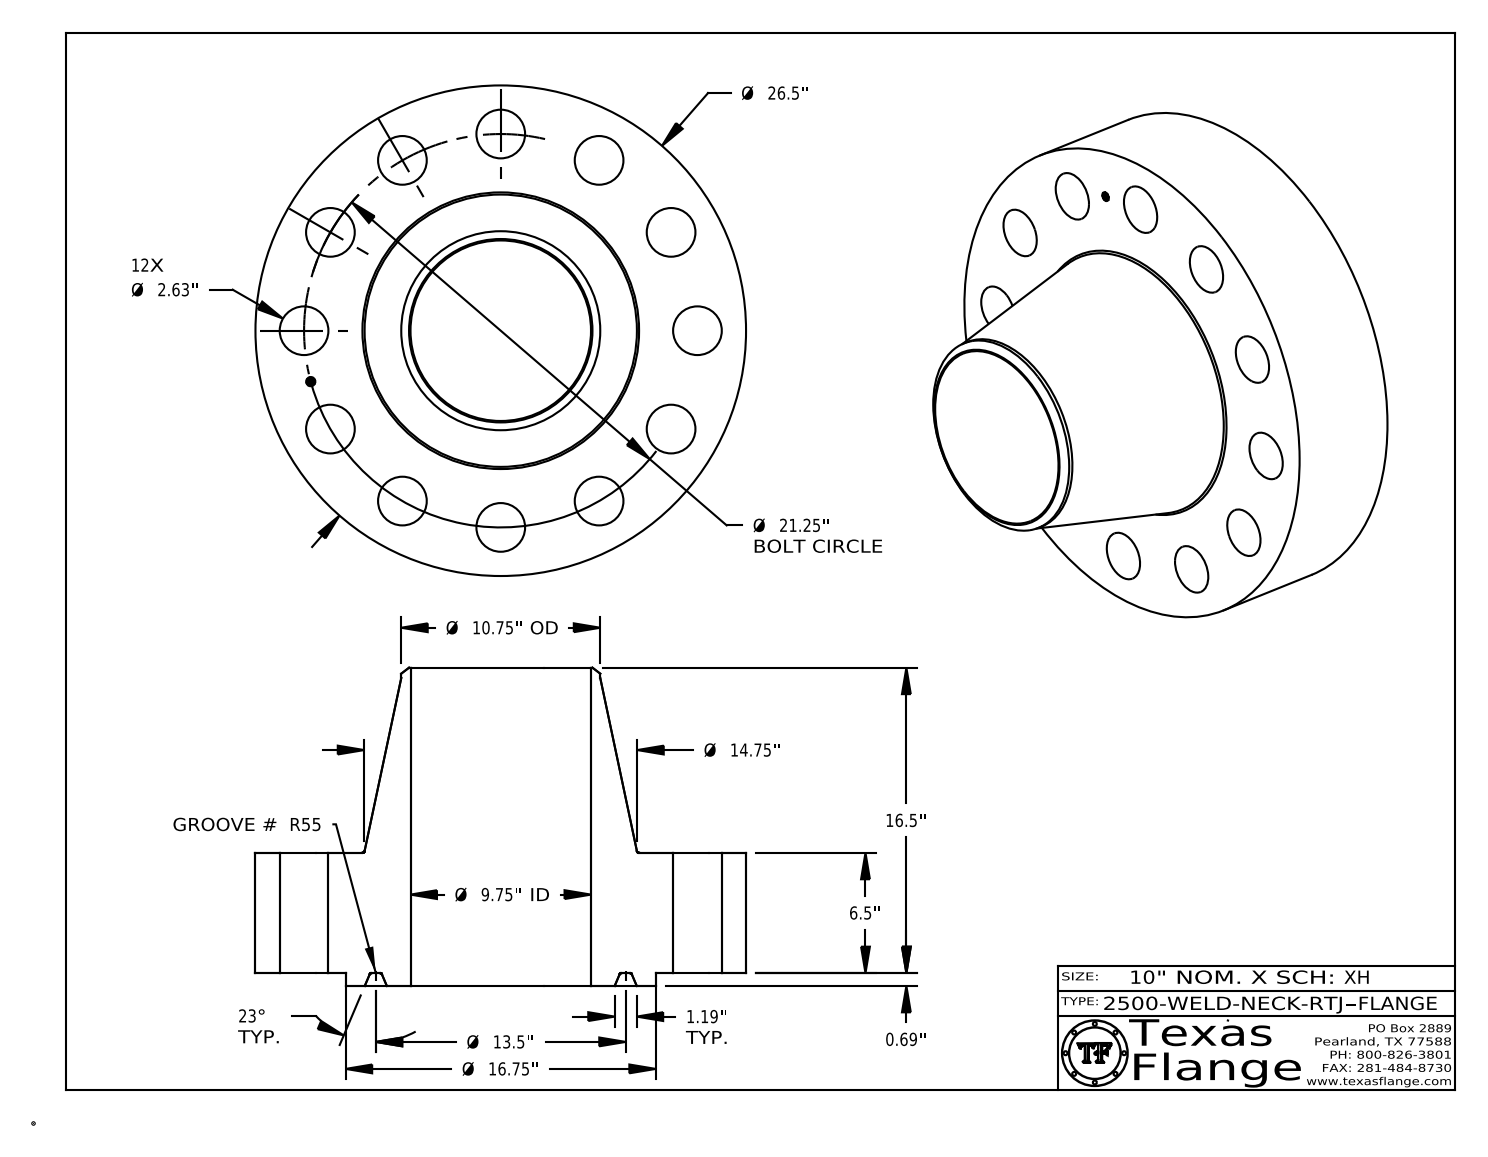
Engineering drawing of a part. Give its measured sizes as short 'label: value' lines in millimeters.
name: 2500-WELD-NECK-RTJ
written by: CATIA V5 STEP AP214 (AUTOMOTIVE_DESIGN)
unit: mm
bodies: 1 solid, 437 faces (371 planar, 52 cylindrical, 14 other)
size: 673.1 × 673.1 × 436.6
volume: 53 540 000 mm³; area: 1 888 000 mm²
holes: 12× ⌀66.8, 1× ⌀12.6, 1× ⌀247.7
bosses: 8× ⌀0.8, 1× ⌀673.1, 1× ⌀425.5, 1× ⌀273.1, 1× ⌀9.9
face distances: 165.1, 17.5, 182.6, 436.6, 419.1, 254, 182.2, 164.7, 0.4, 254.4
hole spacings: 269.9, 139.7, 467.4, 381.7, 521.4, 381.7, 521.4, 539.8
